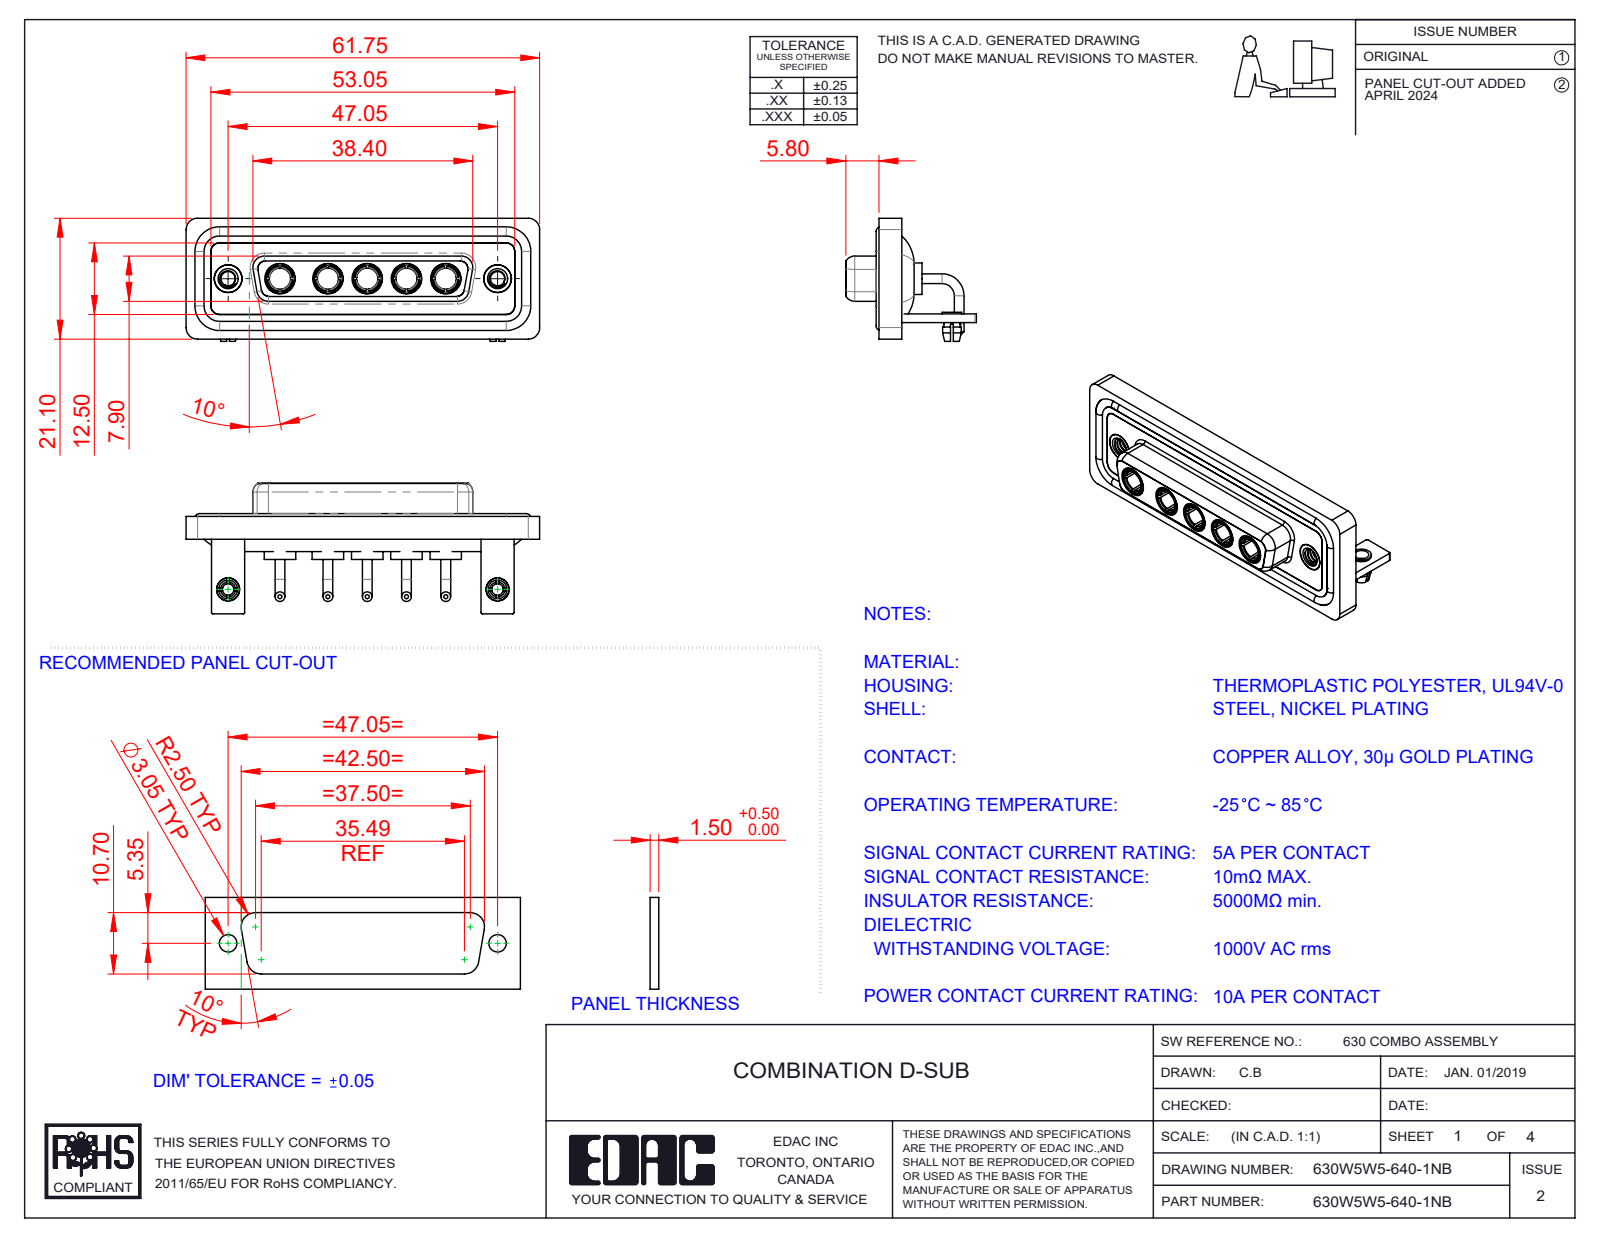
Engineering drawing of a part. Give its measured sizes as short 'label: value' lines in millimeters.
name: 630Combo Stabilizer Bracket_50 Contacts; 630Combo Threaded Rivet_A; 630Combo Shell Rear_25 Contacts; 630Combo Board Lock_50 Contacts (+5 more)
written by: SolidWorks 2023 (CONFIG_CONTROL_DESIGN)
unit: mm
bodies: 21 solids, 910 faces (318 planar, 367 cylindrical, 225 other)
size: 61.75 × 22.8 × 21.5
volume: 8 542 mm³; area: 14 509 mm²
holes: 7× ⌀4.85, 5× ⌀3.7, 5× ⌀5.3, 4× ⌀2.5, 2× ⌀2, 2× ⌀3.2, 2× ⌀4, 2× ⌀4.05, 2× ⌀5
bosses: 10× ⌀1.7, 5× ⌀5.5, 5× ⌀5.2, 5× ⌀4.96, 5× ⌀4.75, 5× ⌀3.75, 4× ⌀1.6, 2× ⌀4.95
rounds: 19× R2, 18× R1.5, 16× R0.25, 8× R1.35, 8× R1.6, 5× R0.5, 5× R2.1, 4× R0.6
face distances: 0.4, 1.8, 1.5, 2.9, 3.7, 4.1, 1.1, 1.4, 1.6, 2.5
hole spacings: 6.86, 9.04, 38.01, 47.05, 6.87, 8.38, 13.72, 13.73
